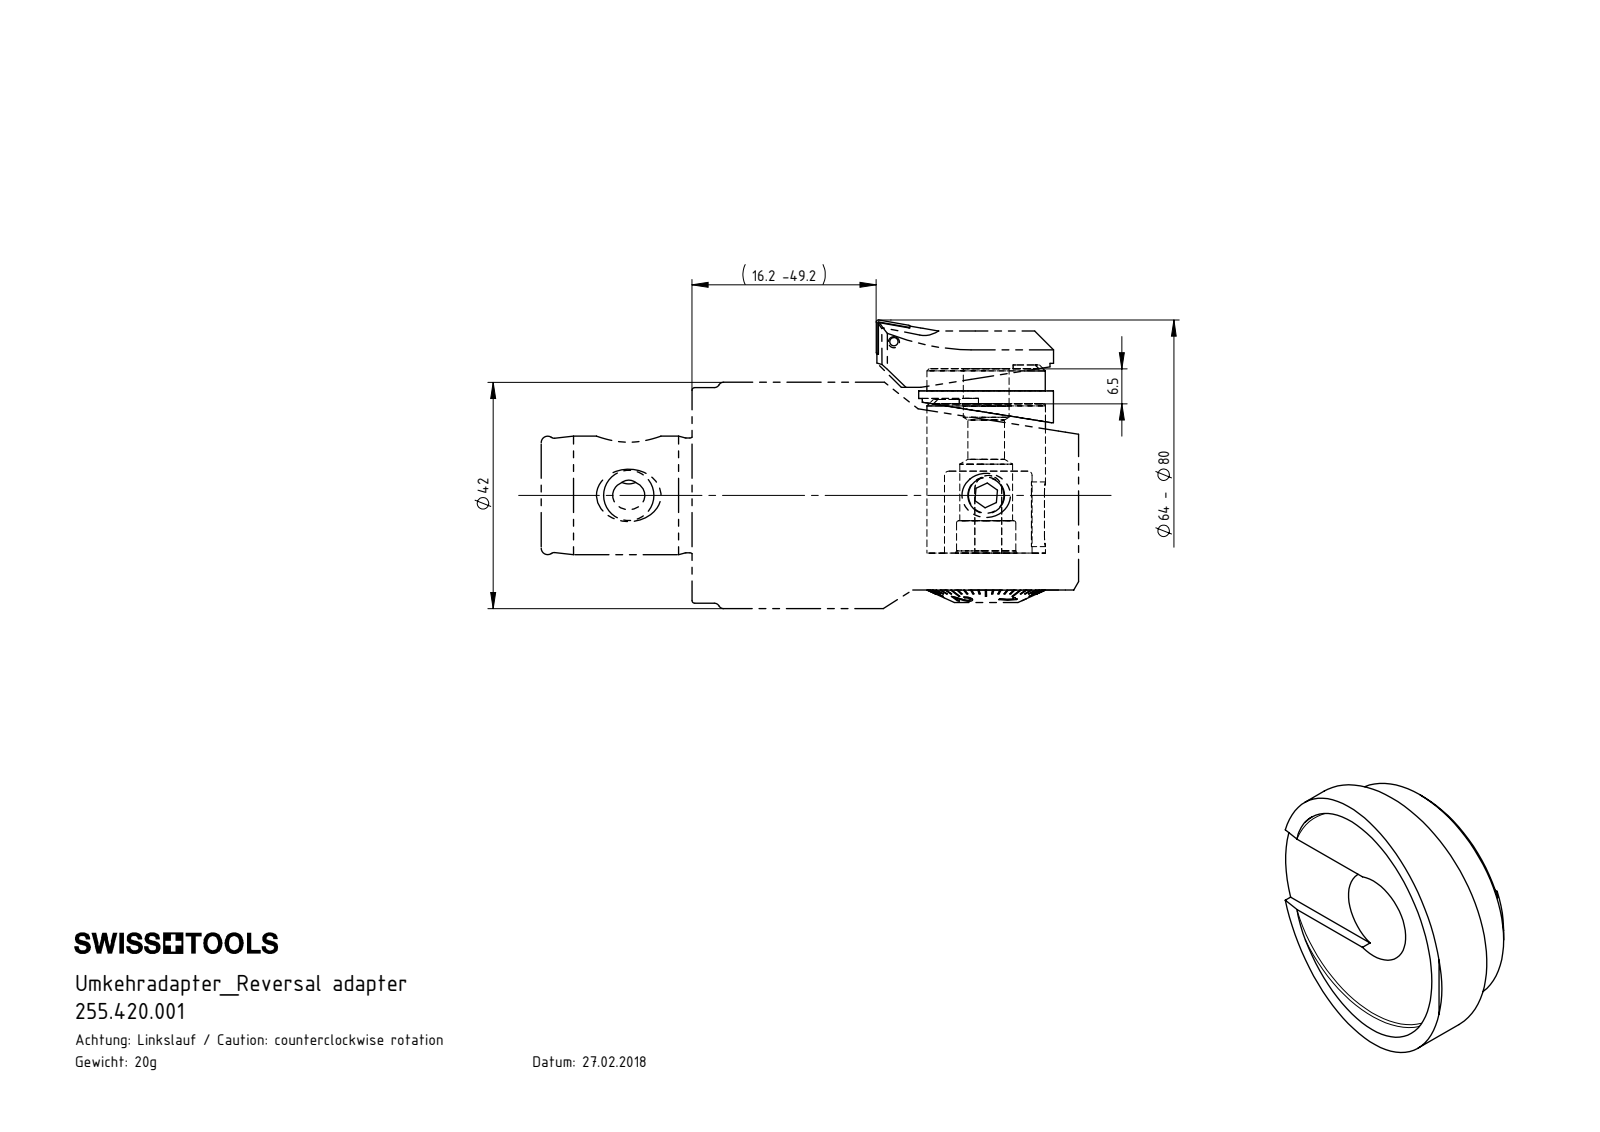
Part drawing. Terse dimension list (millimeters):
name: F42-U00.001.006_B; 255.420.001
written by: SolidWorks 2017 (CONFIG_CONTROL_DESIGN)
unit: mm
bodies: 1 solid, 28 faces (12 planar, 11 cylindrical, 5 other)
size: 25 × 25 × 10.7
volume: 2 498 mm³; area: 1 746 mm²
holes: 1× ⌀8.5, 1× ⌀22
bosses: 1× ⌀25
rounds: 2× R0.5
face distances: 6.5, 4.1, 2.4, 5.5, 1.4, 1, 0.7, 4.8, 6.2, 7.2
